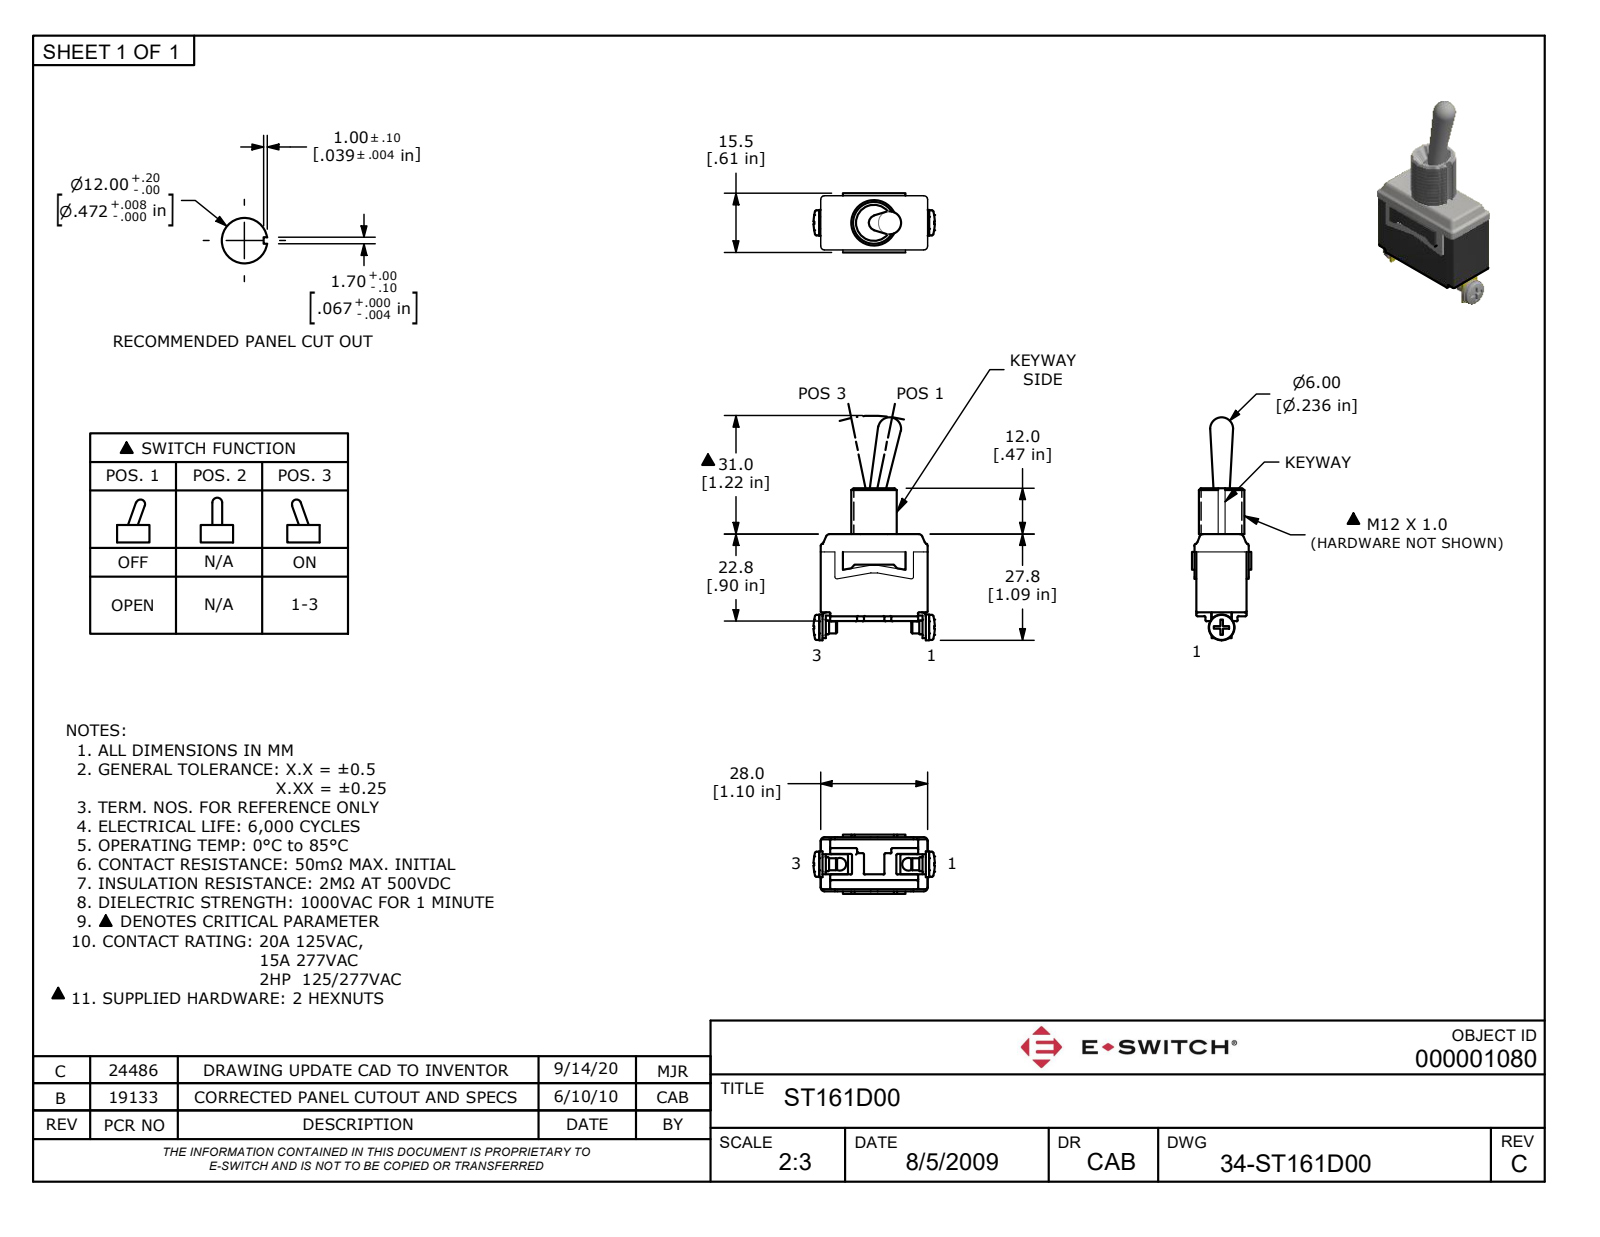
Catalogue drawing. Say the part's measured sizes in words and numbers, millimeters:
The part is named "ST161D00". Its 3-D file was written by "Autodesk Inventor 2022 (AUTOMOTIVE_DESIGN)". It is 1 solid with 431 faces: 177 planar, 127 cylindrical and 127 other. Overall it measures 58.41 by 31.75 by 15.5 millimeters. Its volume is 9 785 cubic millimeters and its surface area 4 158 square millimeters. Round holes: 2 of diameter 2, 1 of diameter 5.4. Round bosses or shafts: 1 of diameter 11.91, 1 of diameter 6.73, 1 of diameter 6.53, 1 of diameter 3.6, 1 of diameter 3.1. Partial cylindrical surfaces (rounded edges, fillets, slot ends): 58 of radius 0.3, 12 of radius 1, 10 of radius 0.5, 4 of radius 0.6, 4 of radius 0.8, 2 of radius 1.1. The main face-to-face distances are 13.1, 0.55, 13.65, 27.94, 1.2, 0.65, 14.3, 14.85, 21.5, 14.2. The hole center spacings are 9, 18.
